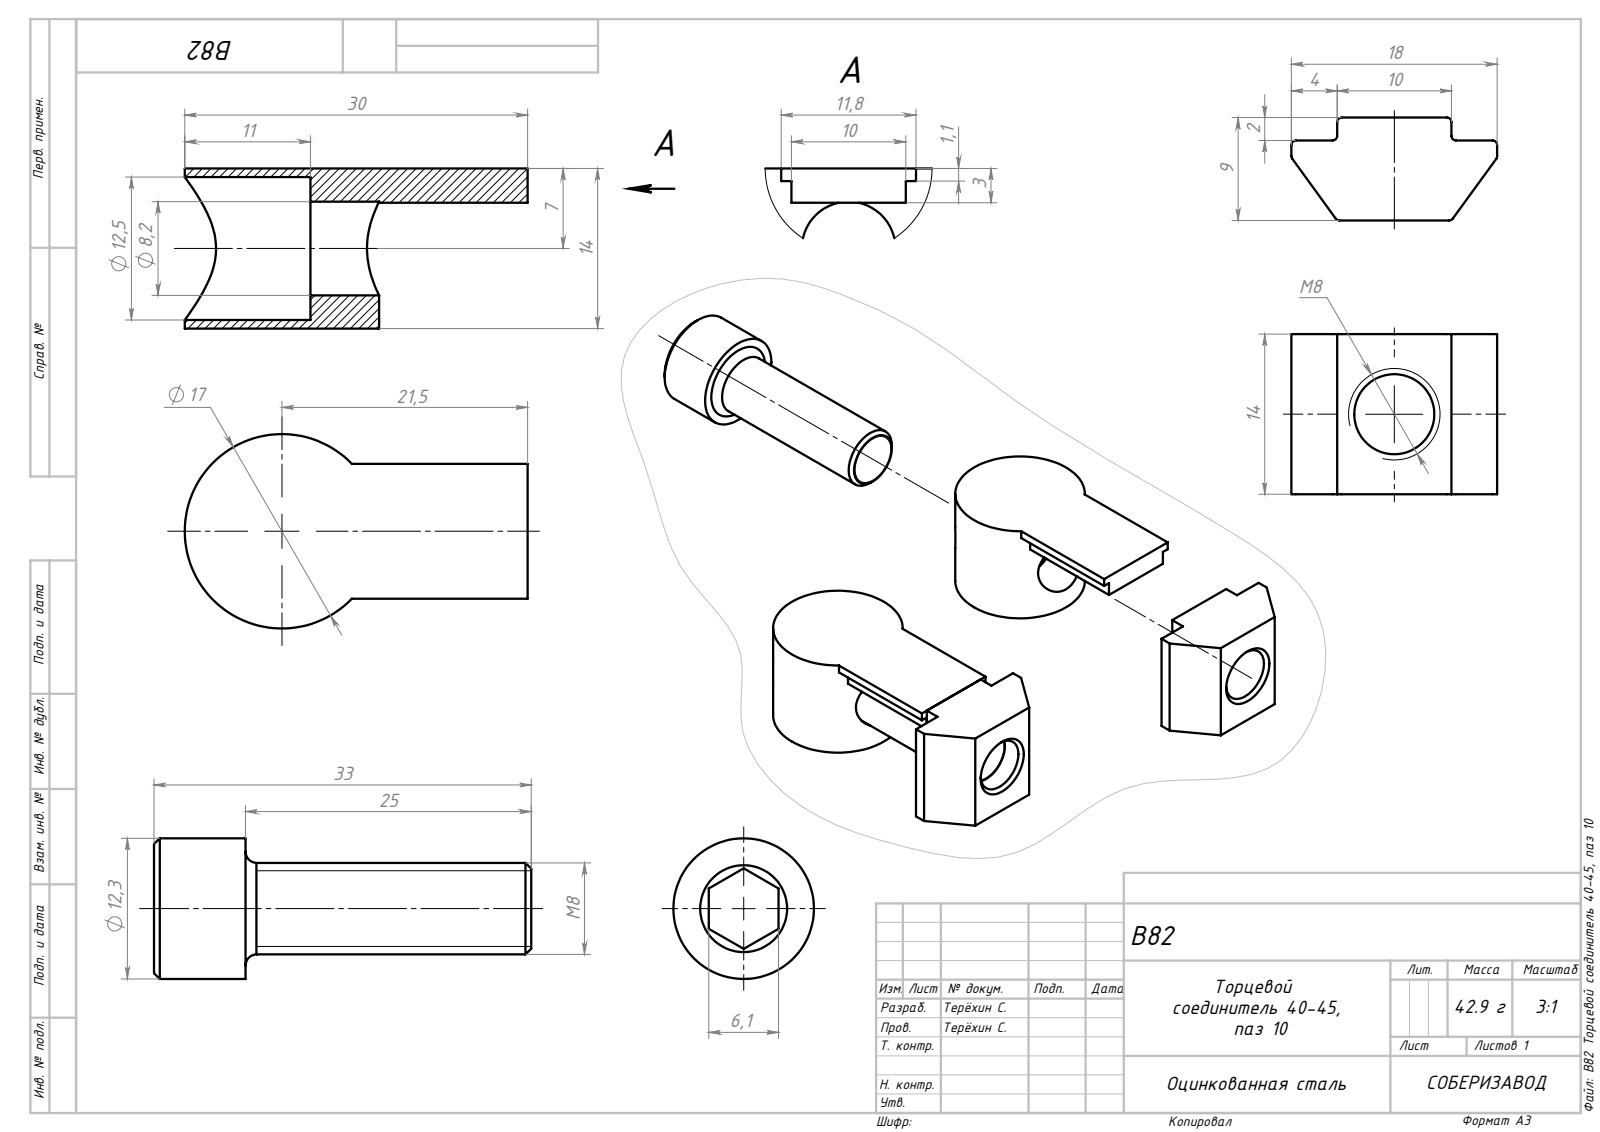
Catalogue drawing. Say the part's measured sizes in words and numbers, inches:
The part is named "SNSD.30.50.45 Болт(В82)_00; B82 Торцевой соединитель 40-45, паз 10; SNSD.30.50.46 Сухарь(B82)_01; SNSD.30.50.44 Вставка(B82), паз10_00". Its 3-D file was written by "SolidWorks 2025 (CONFIG_CONTROL_DESIGN)". It is 3 solids with 59 faces: 34 planar, 13 cylindrical and 12 other. Overall it measures 1.614 by 0.709 by 0.551 inches. Its volume is 0.348 cubic inches and its surface area 6.873 square inches. Round holes: 1 of diameter 0.276, 1 of diameter 0.323, 1 of diameter 0.492. Round bosses or shafts: 1 of diameter 0.669, 1 of diameter 0.484, 1 of diameter 0.315. The main face-to-face distances are 0.551, 0.433, 0.079, 0.118, 0.354, 0.748, 0.827, 1.102, 0.276, 0.394.
